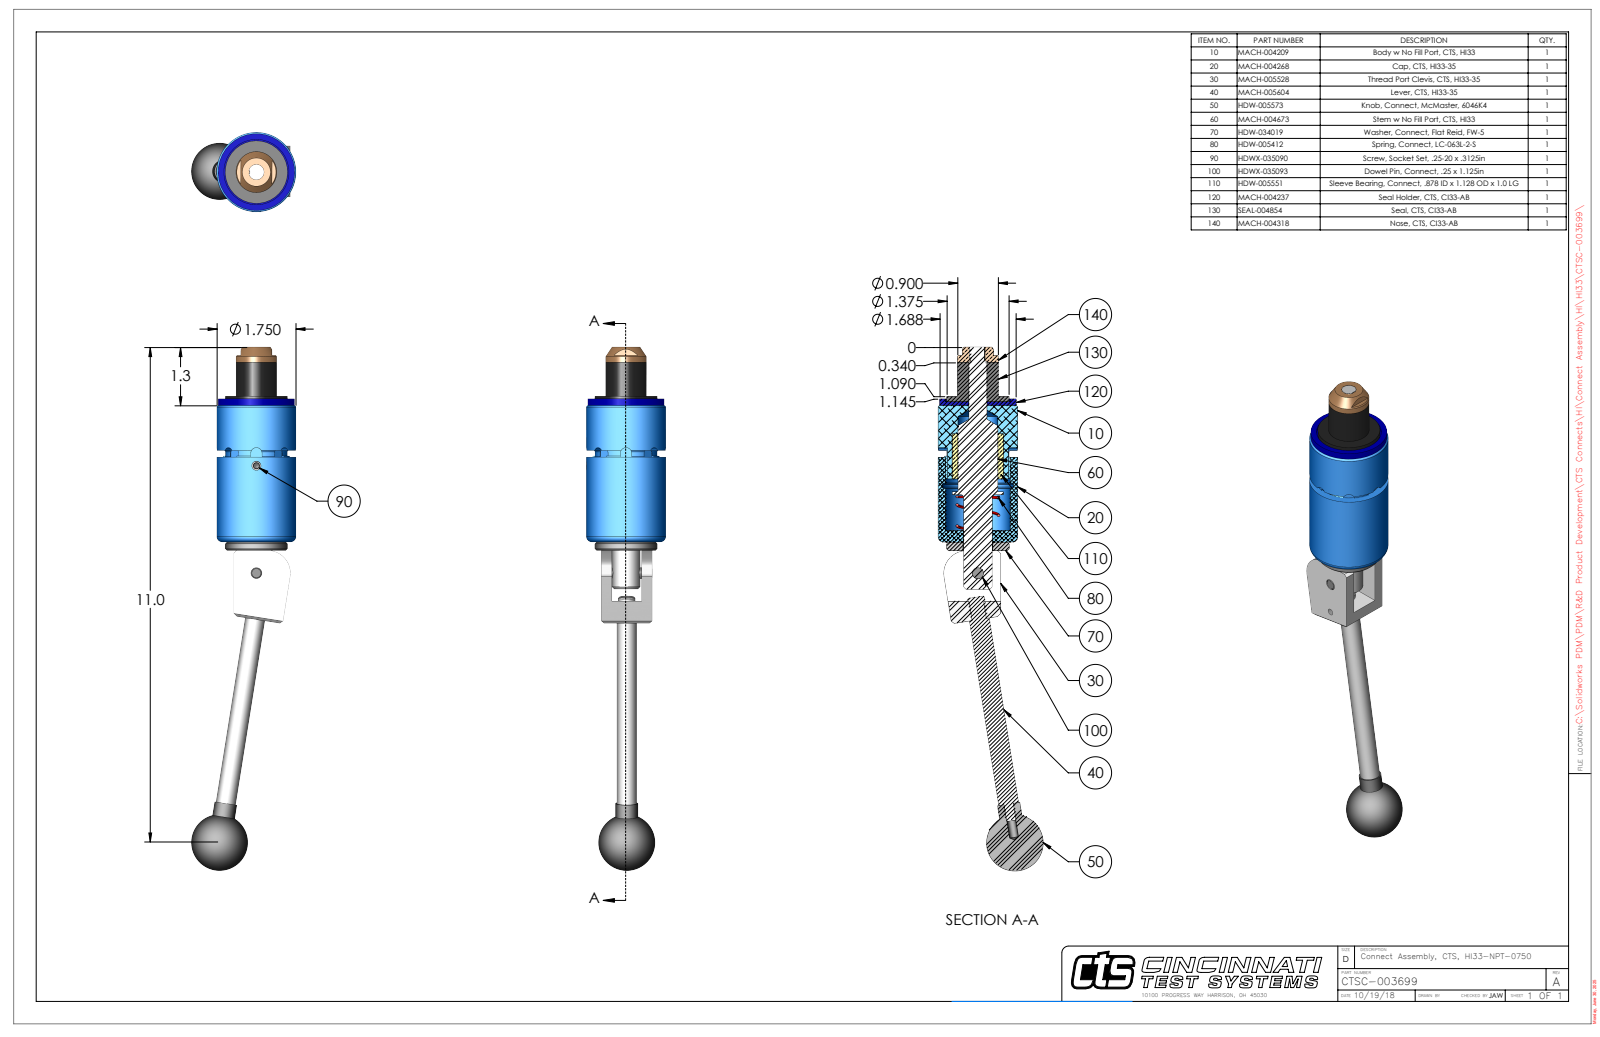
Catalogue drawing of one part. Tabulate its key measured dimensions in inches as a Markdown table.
| quantity | value |
| --- | --- |
| part name | CTSC-003699 |
| STEP written by | SolidWorks 2023 (AUTOMOTIVE_DESIGN) |
| units | inches |
| bodies | 9 solids, 267 faces (102 planar, 110 cylindrical, 55 other) |
| overall size | 11.591 × 2.312 × 1.75 |
| volume | 11.53 in³ |
| surface area | 69.42 in² |
| round holes (diameter × count) | 0.201 × 2, 0.313 × 2, 0.15 × 1, 0.249 × 1, 0.251 × 1, 0.39 × 1, 0.397 × 1, 0.403 × 1, 0.635 × 1, 0.656 × 1, 1.437 × 1 |
| round bosses / shafts (diameter × count) | 0.312 × 2, 0.25 × 2, 1.75 × 1, 1.687 × 1, 1.38 × 1, 1.375 × 1, 0.9 × 1, 0.625 × 1 |
| partial cylindrical surfaces (radius × count) | 0.125 × 4, 0.029 × 2, 0.5 × 1, 0.695 × 1, 0.709 × 1, 0.744 × 1, 0.833 × 1 |
| main face-to-face distances | 0.082, 3.106, 3.024, 1.12, 3.294, 3.212, 0.188, 0.888, 0.232, 0.232 |
| hole center spacings | 0.74, 2.376, 3.116 |
